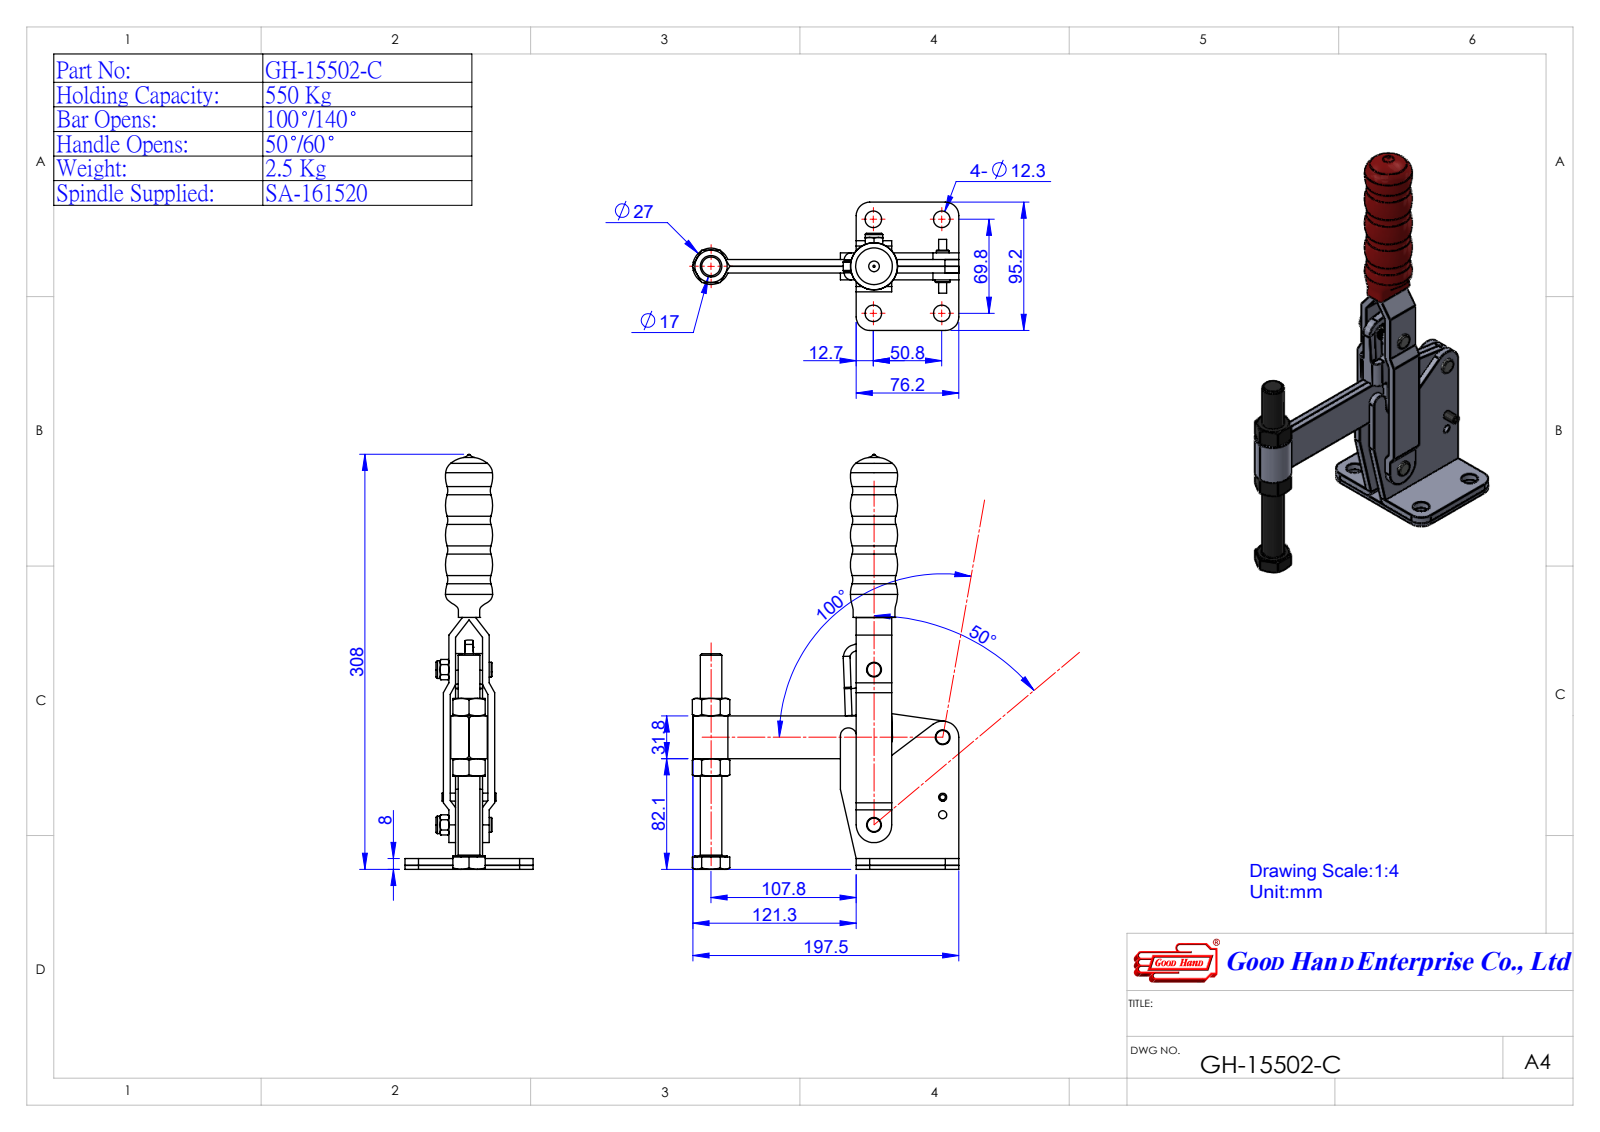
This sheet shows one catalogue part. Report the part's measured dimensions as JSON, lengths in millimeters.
{"part_name": "Group6^GH-15502-C(簡化); Group4^GH-15502-B(簡化)-1; Group3^GH-15502-C(簡化); GH-15502-C(簡化) (+2 more)", "step_written_by": "SolidWorks 2016 (AUTOMOTIVE_DESIGN)", "units": "millimeters", "bodies": {"solids": 5, "faces": 344, "planar": 132, "cylindrical": 102, "other": 110}, "overall_size": [305.8, 197.86, 95.2], "volume_mm3": 396686, "surface_area_mm2": 128143, "round_holes": [[7.5, 4], [12.3, 4], [6, 1], [14, 1], [16, 1], [17, 1]], "round_bosses_or_shafts": [[10, 2], [9.5, 2], [9.45, 2], [27, 1], [24, 1], [16, 1], [7.5, 1], [6, 1]], "partial_cylinders_radius": [[10, 4], [12, 3], [3, 2], [11, 2], [6, 1], [13.2, 1], [15, 1]], "face_to_face_distances": [5, 15, 10, 20, 24, 9, 29, 4, 8, 14], "hole_center_spacings": [50.8, 69.8, 86.33, 125.45, 174.82, 49.25, 50.23, 51.55]}
